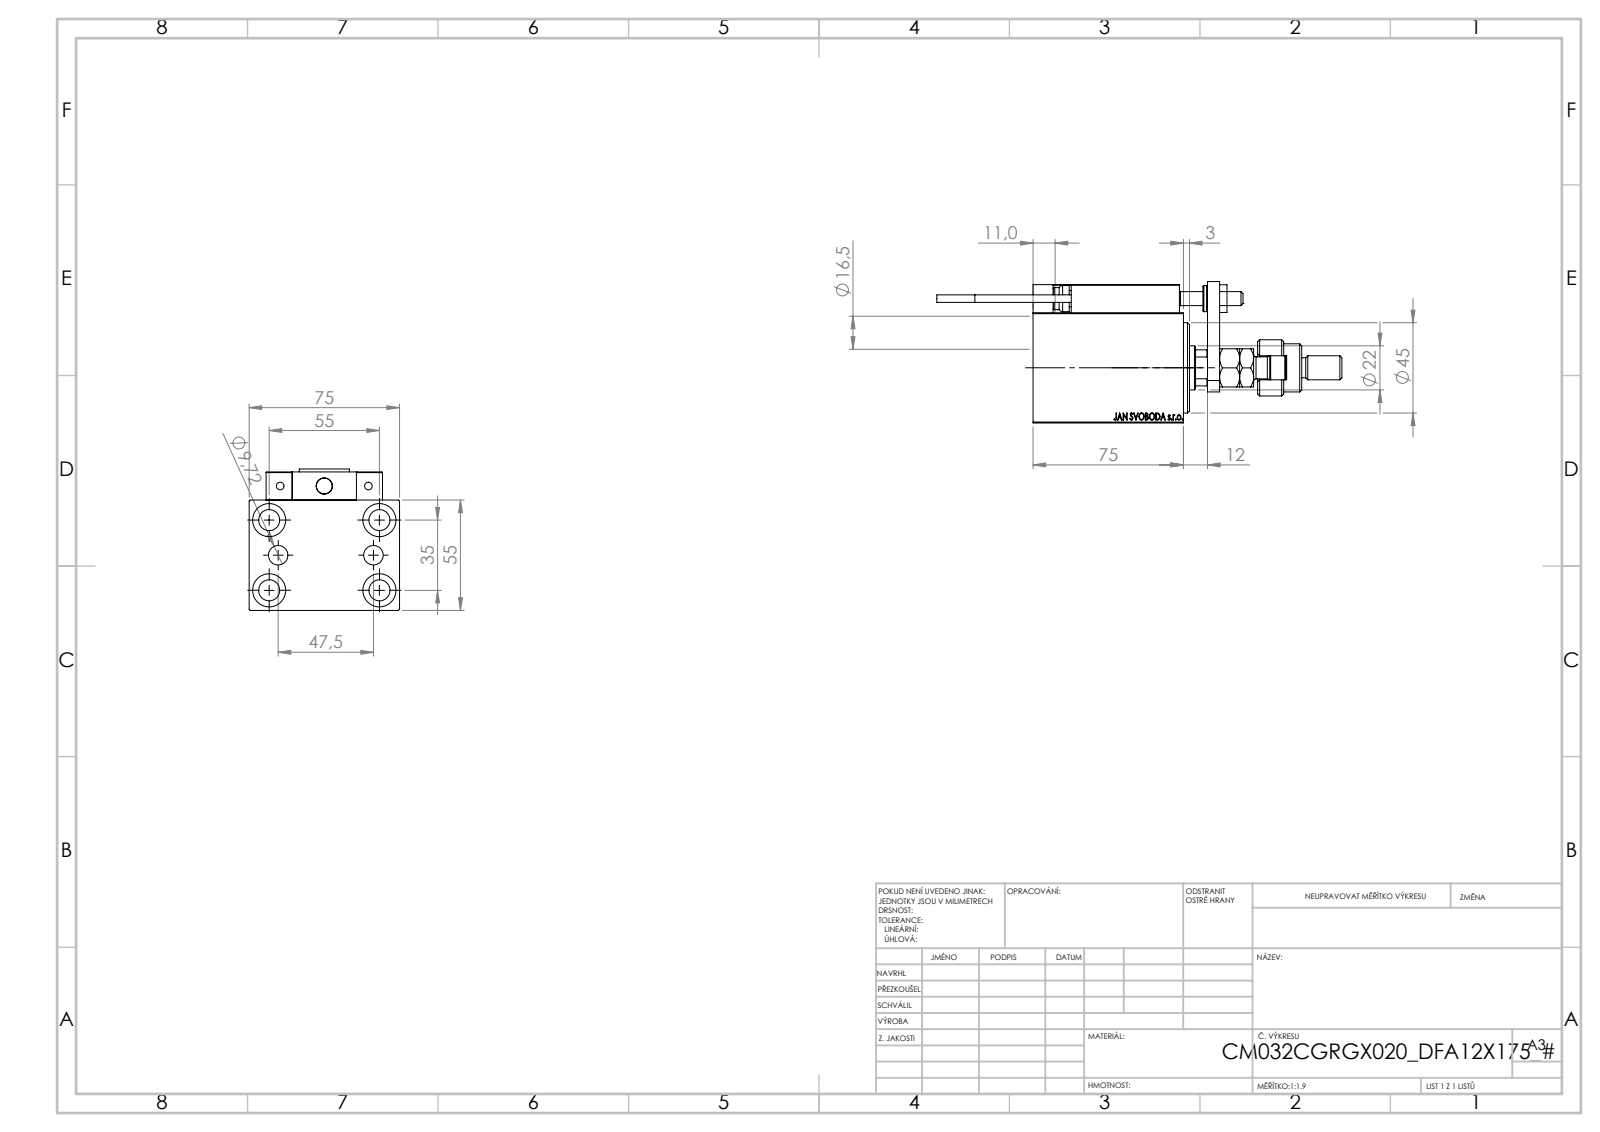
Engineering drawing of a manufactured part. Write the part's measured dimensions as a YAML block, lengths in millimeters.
part_name: "FEMALE_PART_FOR_DFA; MAGNET; V450CM_C_Body; SWITCH X (+7 more)"
step_written_by: "SolidWorks 2019 (CONFIG_CONTROL_DESIGN)"
units: millimeters
bodies: {solids: 25, faces: 1363, planar: 588, cylindrical: 197, other: 578}
overall_size: [202, 75, 70.5]
volume: 331883
surface_area: 94388
round_holes:
  - {diameter: 4, count: 6}
  - {diameter: 8, count: 5}
  - {diameter: 10.5, count: 5}
  - {diameter: 16.5, count: 5}
  - {diameter: 3.2, count: 4}
  - {diameter: 5, count: 2}
  - {diameter: 9.72, count: 2}
  - {diameter: 7, count: 1}
  - {diameter: 22, count: 1}
  - {diameter: 25.5, count: 1}
  - {diameter: 32, count: 1}
  - {diameter: 34, count: 1}
round_bosses_or_shafts:
  - {diameter: 11, count: 2}
  - {diameter: 5, count: 2}
  - {diameter: 3.8, count: 2}
  - {diameter: 28, count: 1}
  - {diameter: 24, count: 1}
  - {diameter: 18, count: 1}
  - {diameter: 13, count: 1}
  - {diameter: 12, count: 1}
partial_cylinders:
  - {radius: 0.3, count: 30}
  - {radius: 3, count: 2}
  - {radius: 9.75, count: 1}
  - {radius: 10.5, count: 1}
face_to_face_distances: [55, 75, 14, 10, 18, 25, 6, 69, 12, 20]
hole_center_spacings: [17.9, 32.6, 54.16, 11.37, 20, 23.75, 27.07, 29.59]
